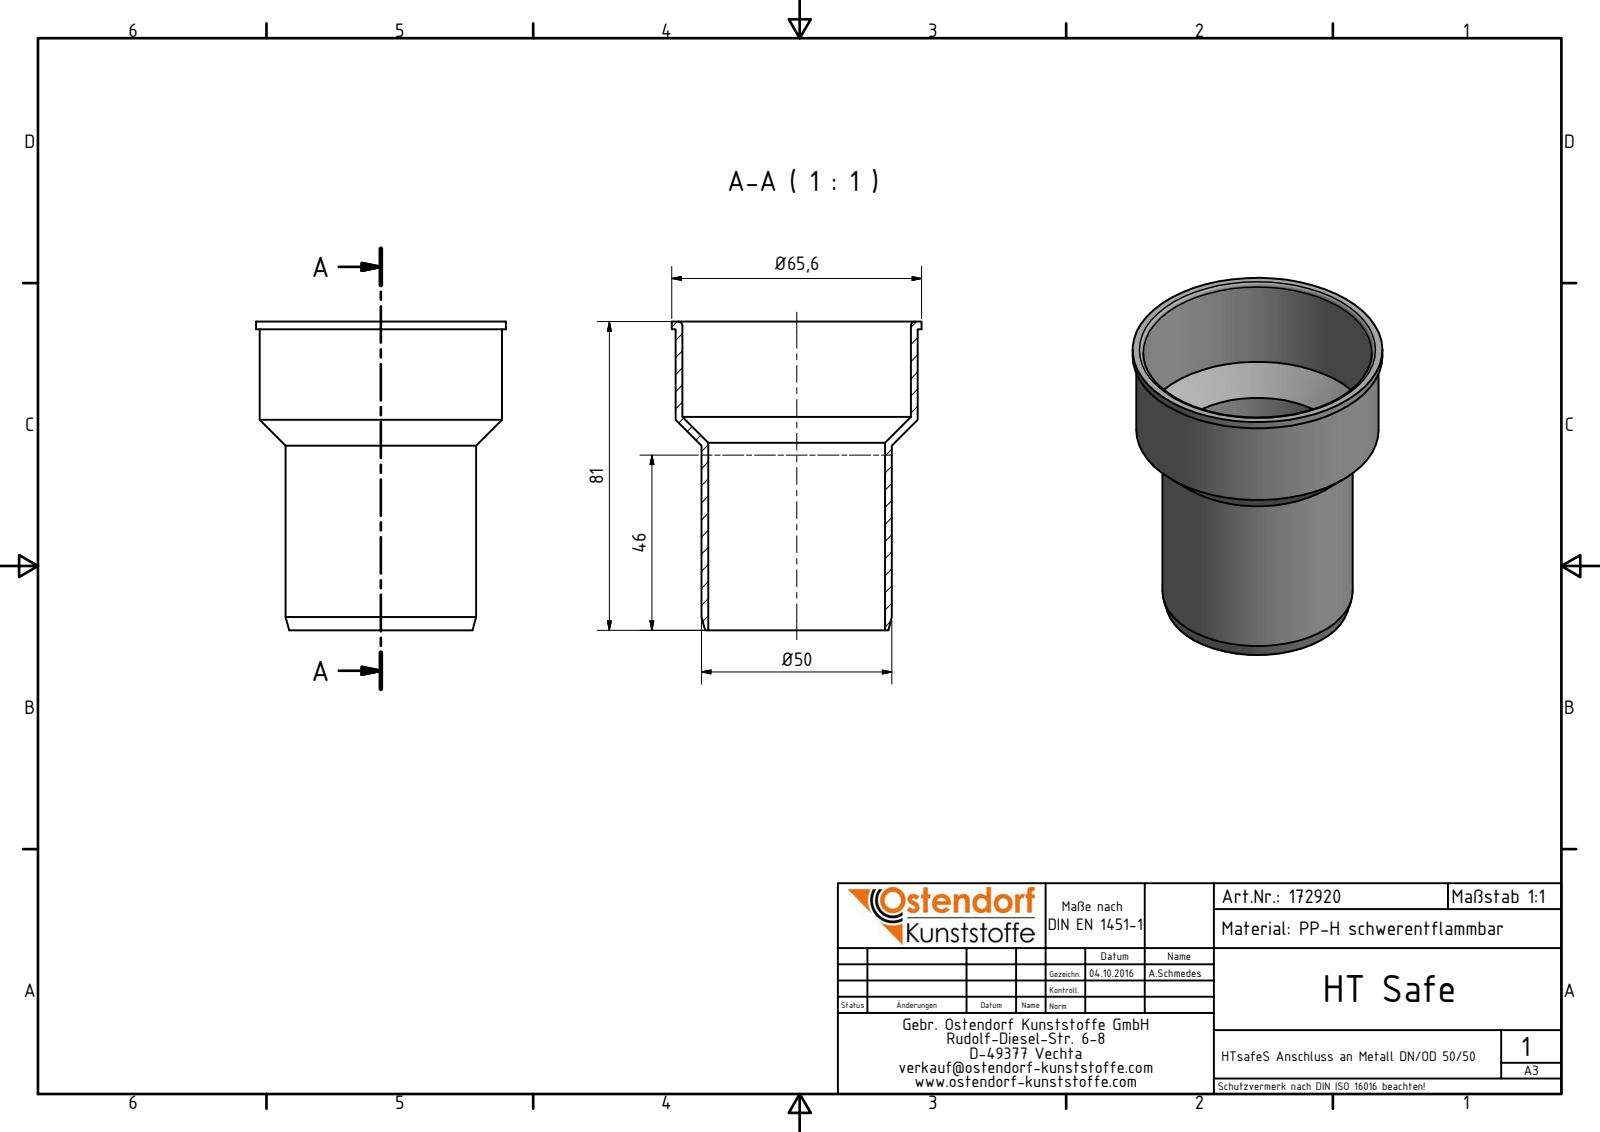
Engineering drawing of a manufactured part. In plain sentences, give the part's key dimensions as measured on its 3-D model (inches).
The part is named "172920 HTsafeS DN_OD 50_50". Its 3-D file was written by "Autodesk Inventor 2016 (AUTOMOTIVE_DESIGN)". It is 1 solid with 12 faces: 3 planar, 5 cylindrical and 4 other. Overall it measures 3.189 by 2.583 by 2.583 inches. Its volume is 1.542 cubic inches and its surface area 44.62 square inches. Round holes: 1 of diameter 1.827, 1 of diameter 2.362. Round bosses or shafts: 1 of diameter 2.583, 1 of diameter 2.504, 1 of diameter 1.969. The main face-to-face distances are 0.079, 3.11, 3.189.
